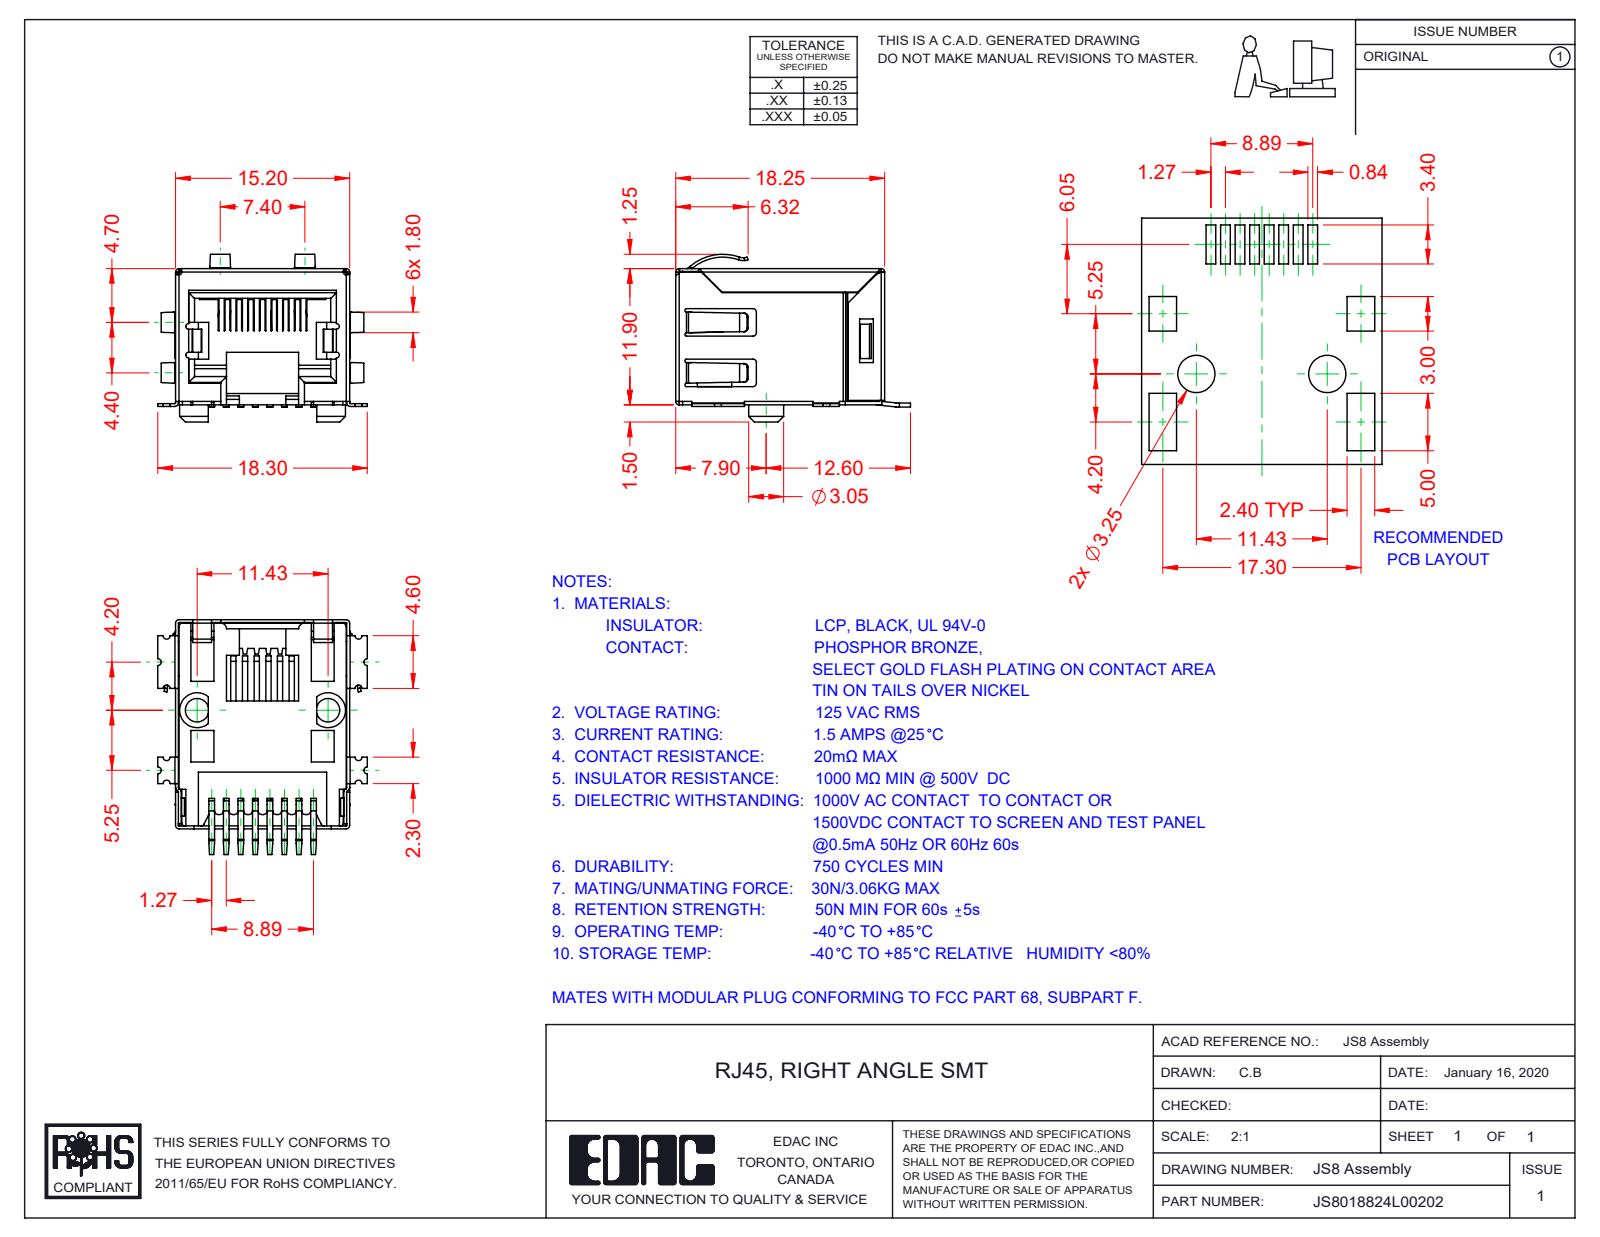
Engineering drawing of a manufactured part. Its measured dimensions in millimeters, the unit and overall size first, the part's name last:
Units: millimetres
Overall size (bounding box): 20.5 × 18.3 × 14.65
Partial cylindrical surfaces — rounded edges, fillets, slot ends (radius × count): R0.3 ×59, R0.25 ×19, R0.5 ×18, R0.2 ×17, R0.15 ×8, R0.75 ×7, R1 ×4, R1.25 ×3
Main face-to-face distances: 14.65, 14.95, 14.9, 1, 0.35, 14.7, 0.75, 10.9, 1.1, 15.2
Volume: 1 308 mm³ · Surface area: 4 634 mm²
Bodies: 10 solids, 976 faces (602 planar, 314 cylindrical, 60 other)
Part name (STEP PRODUCT): S8 Contacts; RJS8018824L00202; S8 Shield; S8 Insulator
STEP written by: SolidWorks 2016 (CONFIG_CONTROL_DESIGN)
